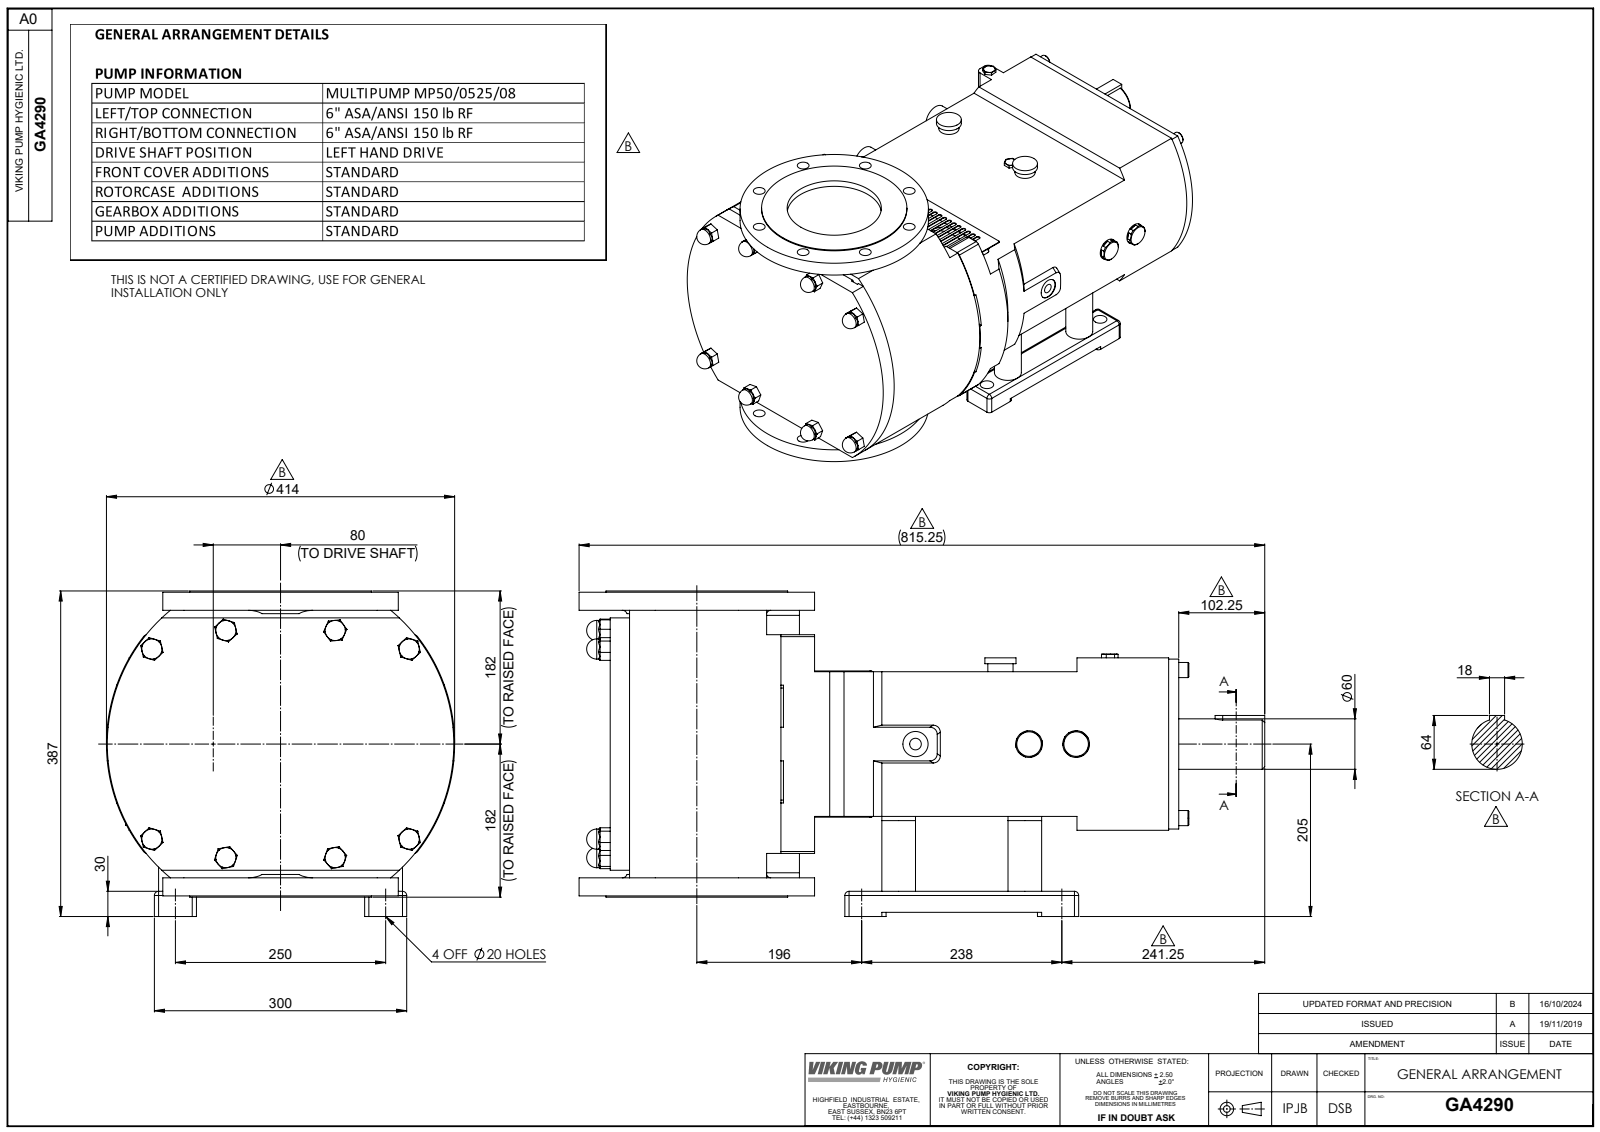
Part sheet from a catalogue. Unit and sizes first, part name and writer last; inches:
Units: inches
Overall size (bounding box): 32.096 × 16.299 × 15.236
Round holes (diameter × count): ⌀0.689 ×8, ⌀0.787 ×4, ⌀0.453 ×2, ⌀1.378 ×2, ⌀0.545 ×1, ⌀1.181 ×1, ⌀5.512 ×1
Round bosses / shafts (diameter × count): ⌀1.575 ×8, ⌀0.945 ×8, ⌀0.709 ×4, ⌀6.654 ×2, ⌀3.15 ×2, ⌀2.756 ×2, ⌀2.677 ×2, ⌀1.457 ×2
Partial cylindrical surfaces — rounded edges, fillets, slot ends (radius × count): R0.118 ×52, R0.197 ×36, R0.236 ×22, R0.315 ×12, R0.079 ×4, R0.6 ×2, R0.354 ×1, R6.083 ×1
Main face-to-face distances: 6.772, 0.65, 7.421, 26.614, 7.323, 0.906, 3.071, 9.646, 3.72, 11.142
Hole centre spacings: 4.75, 6.718, 8.777, 3.635, 3.636, 9.5, 2.435, 2.635
Volume: 3 323 in³ · Surface area: 2 404 in²
Bodies: 1 solid, 1157 faces (511 planar, 404 cylindrical, 242 other)
Part name (STEP PRODUCT): GA4290; Copy of CP50L-0525 ASA150 V LHD^GA4290
STEP written by: SolidWorks 2023 (AUTOMOTIVE_DESIGN)
